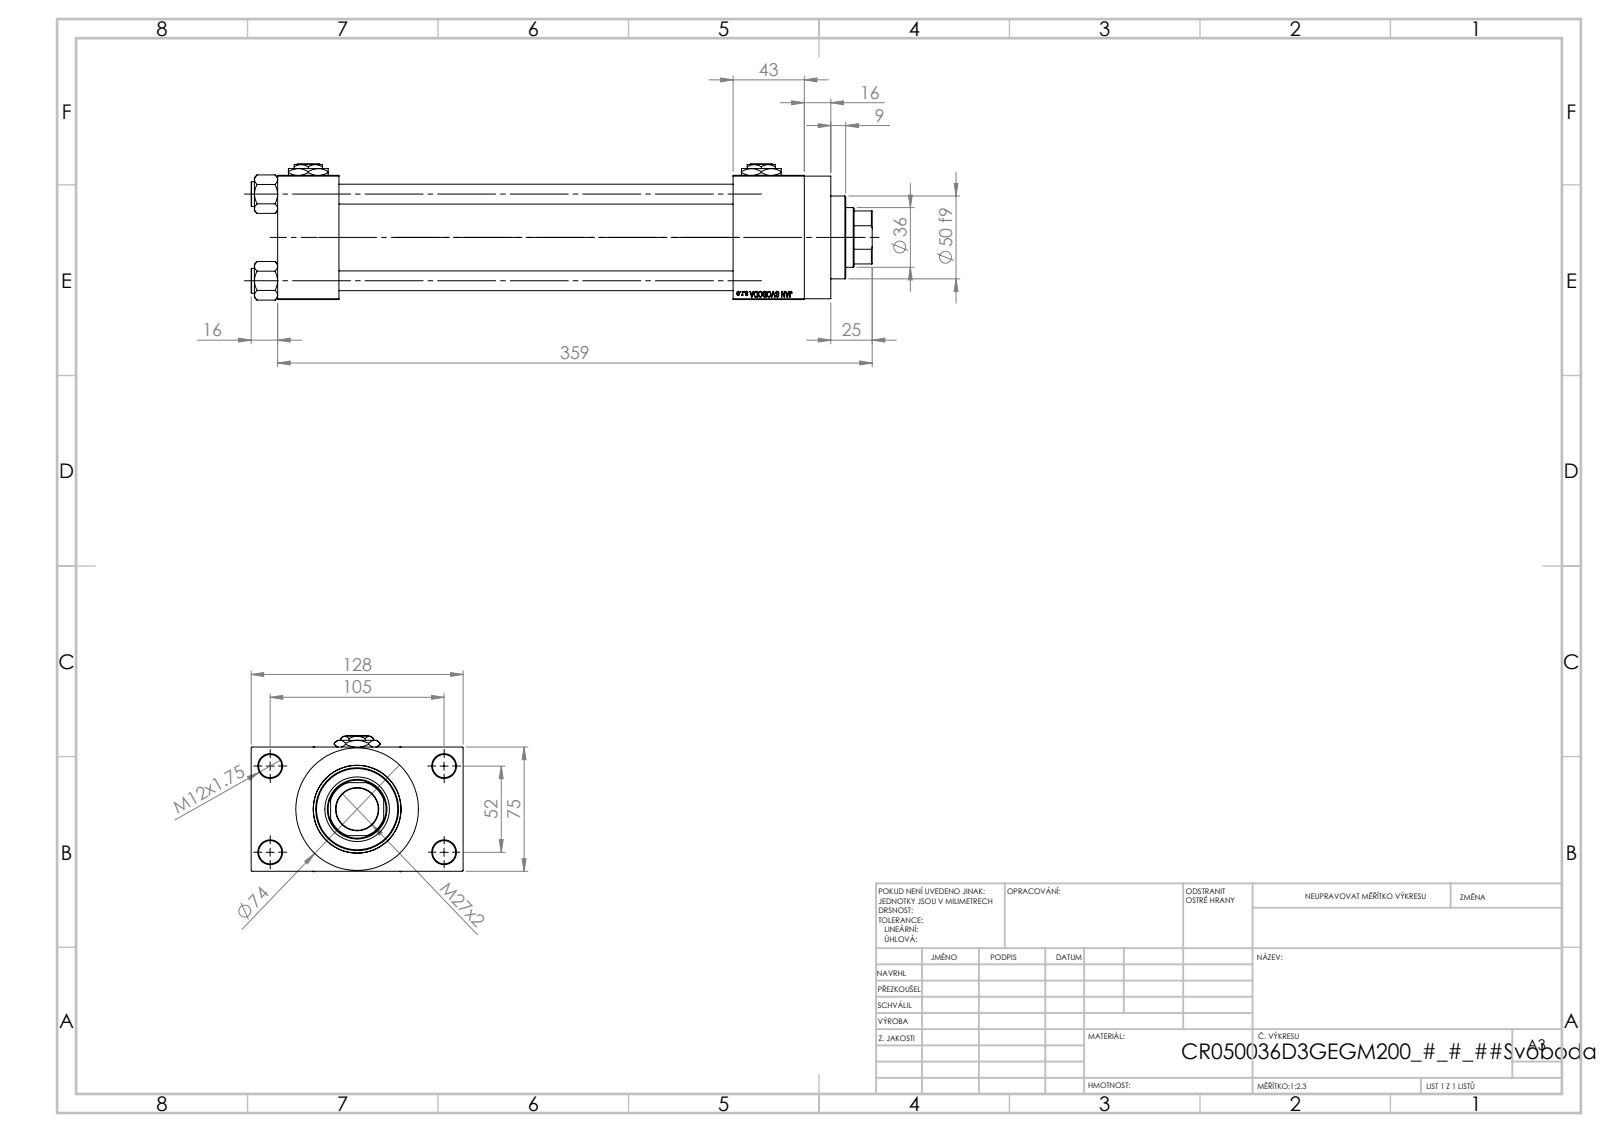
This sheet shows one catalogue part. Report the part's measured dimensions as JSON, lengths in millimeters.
{"part_name": "V215CR_VCP_D; NUT_M5_D; V215CR_D_Body; V215CR_D_TYCINKA (+2 more)", "step_written_by": "SolidWorks 2019 (CONFIG_CONTROL_DESIGN)", "units": "millimeters", "bodies": {"solids": 13, "faces": 1205, "planar": 545, "cylindrical": 100, "other": 560}, "overall_size": [375, 128, 82.27], "volume_mm3": 1177000, "surface_area_mm2": 285470, "round_holes": [[12, 4], [14, 4], [7, 2], [20.96, 2], [30, 2], [25.5, 1], [36, 1], [39, 1], [41, 1], [53, 1]], "round_bosses_or_shafts": [[15, 4], [74, 1], [56, 1], [50, 1]], "partial_cylinders_radius": [[17.5, 1]], "face_to_face_distances": [75, 238, 37, 275, 26.5, 101.5, 318, 43, 281, 16], "hole_center_spacings": [26.35, 36.98, 52.3, 58.43, 58.59, 78.65, 94.37, 52]}
